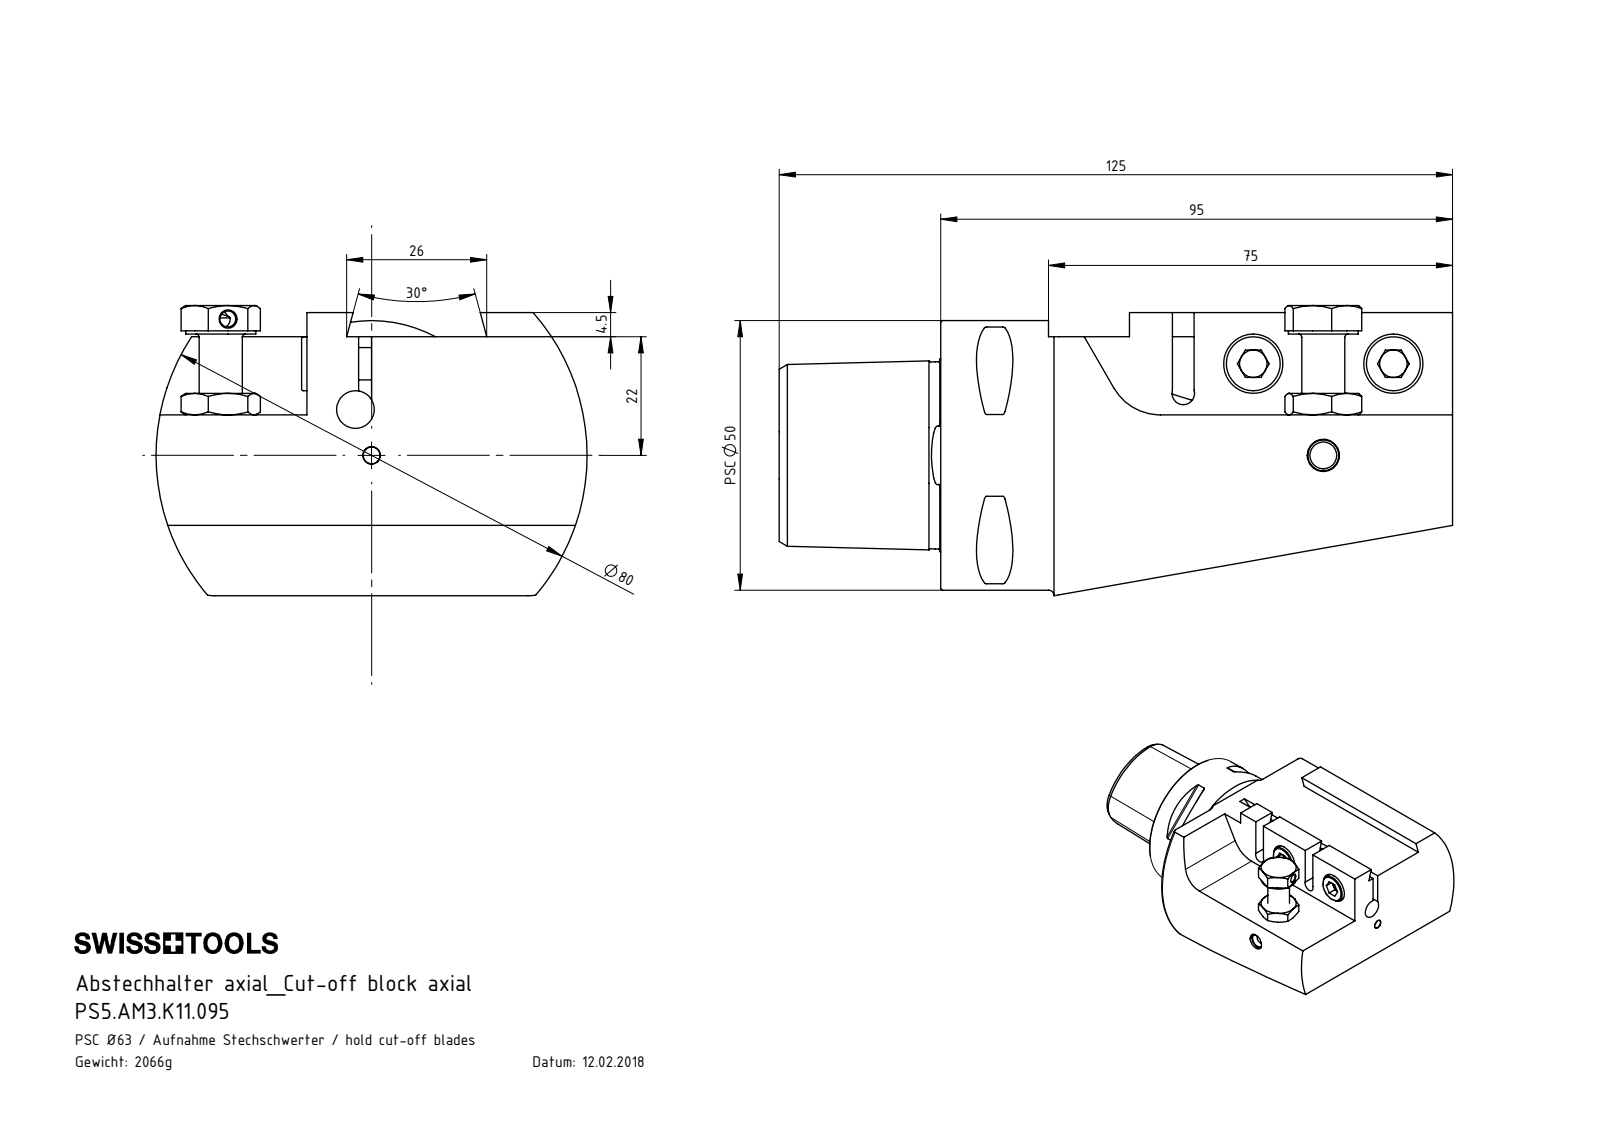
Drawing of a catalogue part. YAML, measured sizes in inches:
part_name: "ISO 4762 - M6 x 16_PreviewCfg; AM3-ER1.001.020_PreviewCfg; ISO 4035 - M8_PreviewCfg; KVT_MB_600_060 (+2 more)"
step_written_by: "SolidWorks 2015 (AUTOMOTIVE_DESIGN)"
units: inches
bodies: {solids: 7, faces: 354, planar: 103, cylindrical: 85, other: 166}
overall_size: [4.921, 3.15, 2.12]
volume: 16.13
surface_area: 65.9
round_holes:
  - {diameter: 0.197, count: 3}
  - {diameter: 0.252, count: 3}
  - {diameter: 0.157, count: 2}
  - {diameter: 0.276, count: 2}
  - {diameter: 0.433, count: 2}
  - {diameter: 0.118, count: 1}
  - {diameter: 0.124, count: 1}
  - {diameter: 0.24, count: 1}
  - {diameter: 0.256, count: 1}
  - {diameter: 0.335, count: 1}
  - {diameter: 0.571, count: 1}
  - {diameter: 0.827, count: 1}
round_bosses_or_shafts:
  - {diameter: 0.236, count: 3}
  - {diameter: 0.394, count: 2}
  - {diameter: 1.969, count: 1}
  - {diameter: 0.512, count: 1}
  - {diameter: 0.315, count: 1}
partial_cylinders:
  - {radius: 0.02, count: 8}
  - {radius: 0.083, count: 2}
  - {radius: 0.157, count: 1}
  - {radius: 0.394, count: 1}
  - {radius: 1.575, count: 1}
  - {radius: 2.047, count: 1}
face_to_face_distances: [0.571, 2.913, 0.748, 0.177, 0.472, 0.827, 3.74, 1.181, 1.024, 0.094]
hole_center_spacings: [0.843, 1.024, 2.913, 0.355, 1.931, 2.323, 3.346, 3.916]
